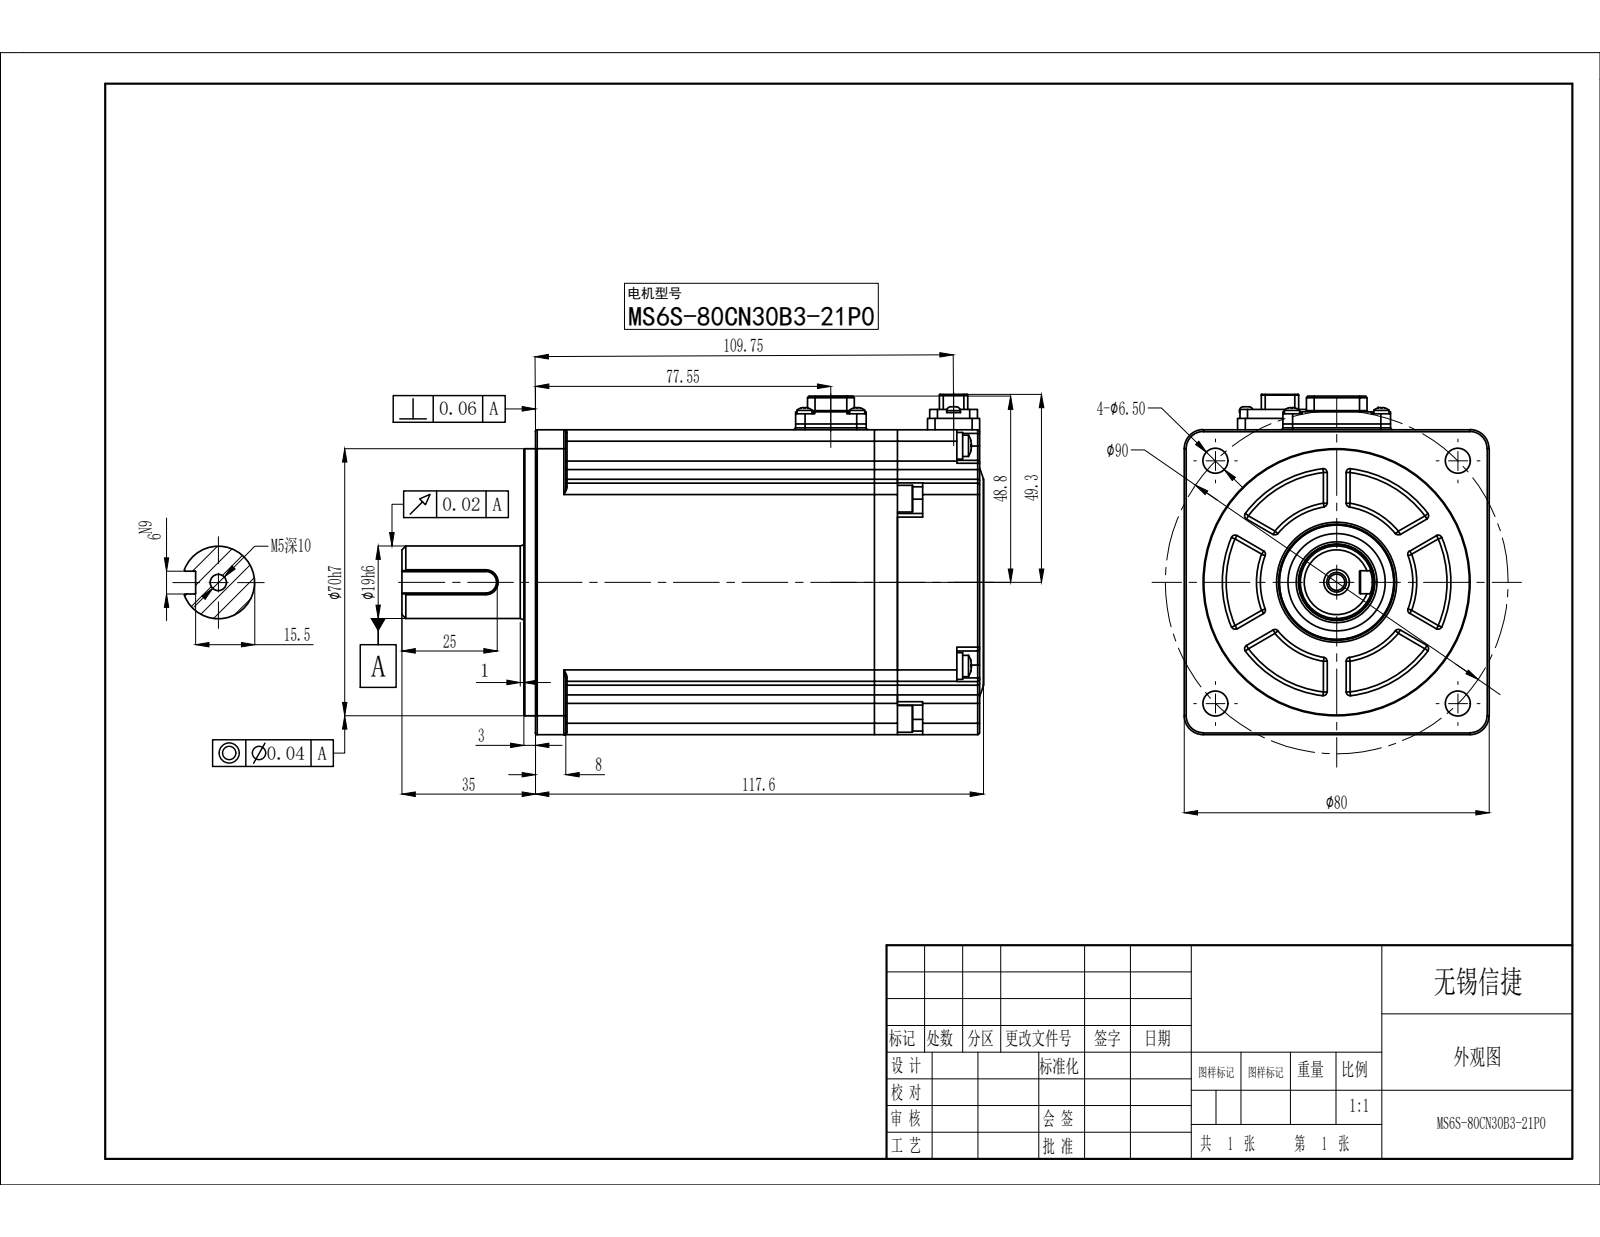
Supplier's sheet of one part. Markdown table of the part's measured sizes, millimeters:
| quantity | value |
| --- | --- |
| STEP written by | SolidWorks 2016 (CONFIG_CONTROL_DESIGN) |
| units | millimeters |
| bodies | 0 solids, 809 faces (381 planar, 278 cylindrical, 150 other) |
| overall size | 152.6 × 89.3 × 80 |
| round holes (diameter × count) | 2.1 × 4, 6.5 × 4, 1.6 × 2, 4.2 × 1, 20 × 1 |
| round bosses / shafts (diameter × count) | 7 × 8, 5.6 × 4, 4 × 4, 3.5 × 2, 70 × 1, 42 × 1, 30 × 1, 26.9 × 1 |
| partial cylindrical surfaces (radius × count) | 1 × 50, 0.5 × 39, 3 × 17, 0.2 × 15, 0.3 × 14, 2 × 12, 3.75 × 8, 0.6 × 4 |
| main face-to-face distances | 80, 14, 66, 116.6, 1, 117.6, 52, 3, 21.6, 120.6 |
| hole center spacings | 45, 63.64, 8, 16.6, 18.43, 90, 23.5, 28.67 |
